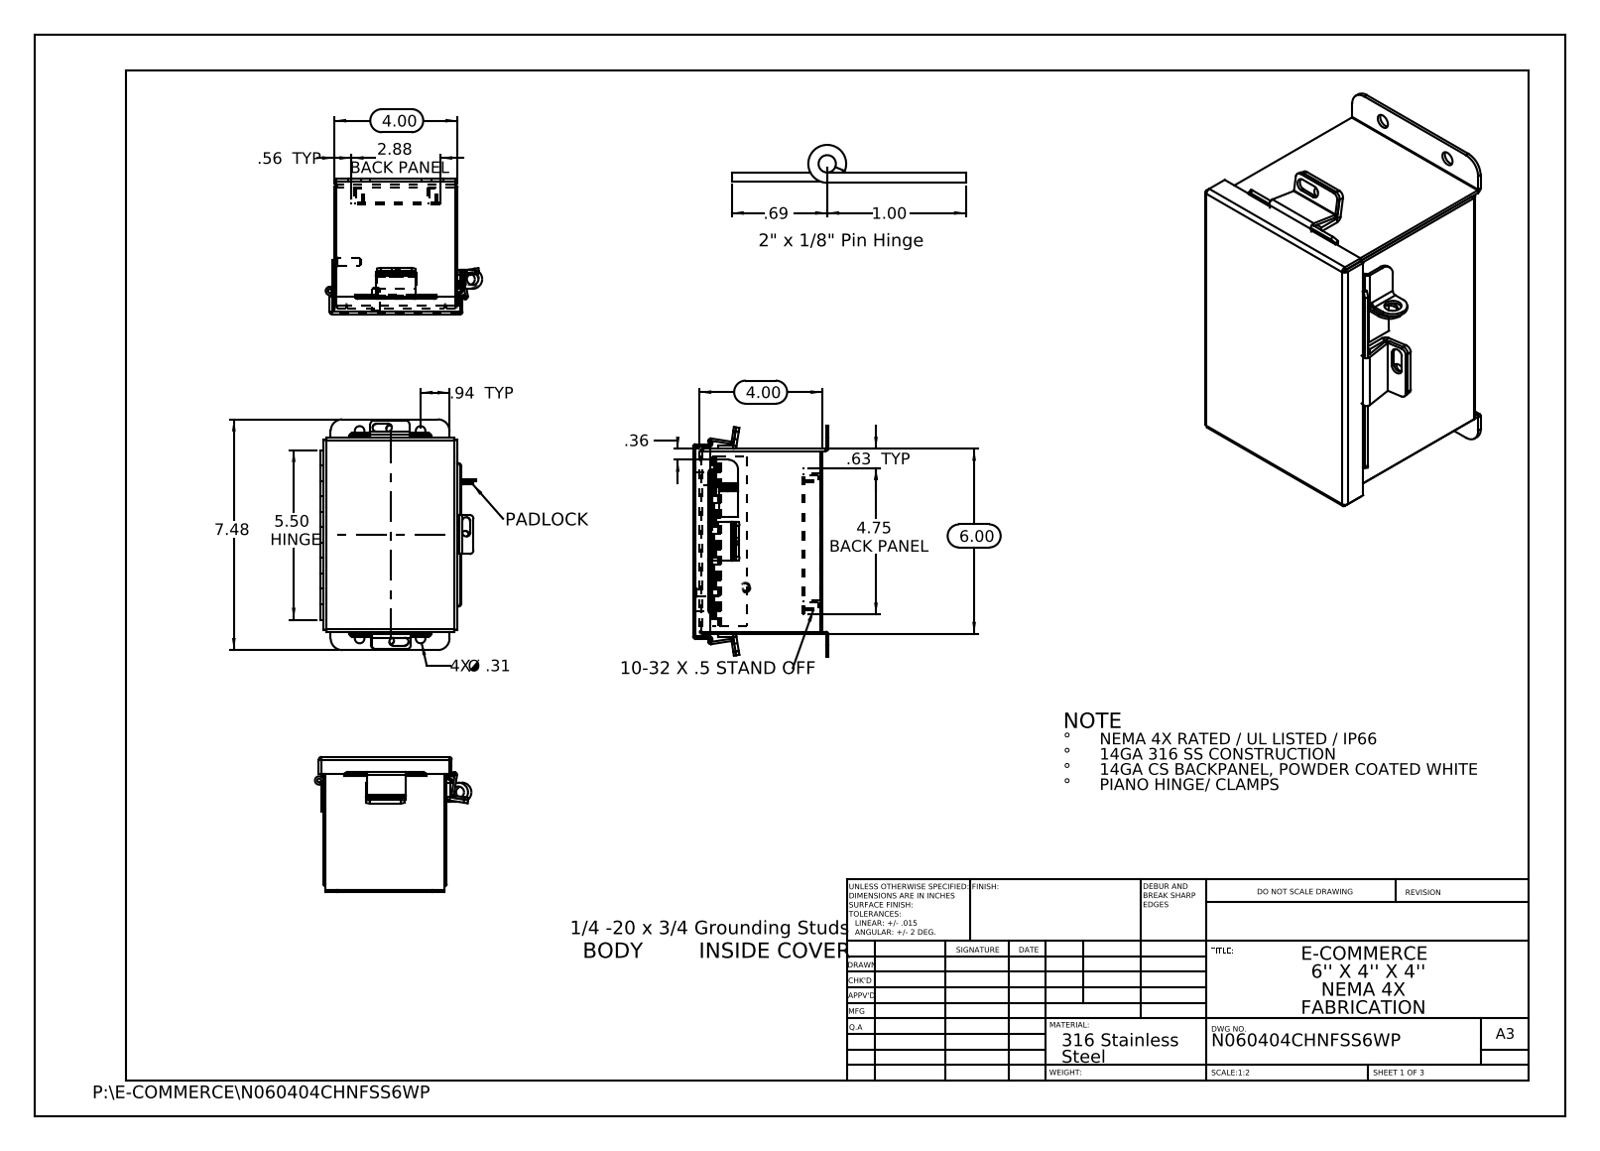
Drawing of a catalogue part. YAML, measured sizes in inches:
part_name: "N060404CHNFSS6WP JIC_Cover_Template; HW-CLH-JH-20154; N060404CHNFSS6WP _JIC Hinge; N060404CHNFSS6WP JIC Enclosure Template (+8 more)"
step_written_by: "SolidWorks 2013 (CONFIG_CONTROL_DESIGN)"
units: inches
bodies: {solids: 21, faces: 540, planar: 343, cylindrical: 177, other: 20}
overall_size: [7.476, 5.072, 4.39]
volume: 14.09
surface_area: 392.2
round_holes:
  - {diameter: 0.25, count: 7}
  - {diameter: 0.187, count: 4}
  - {diameter: 0.312, count: 4}
  - {diameter: 0.125, count: 1}
  - {diameter: 0.125, count: 1}
  - {diameter: 0.373, count: 1}
  - {diameter: 0.375, count: 1}
round_bosses_or_shafts:
  - {diameter: 0.313, count: 4}
  - {diameter: 0.315, count: 2}
  - {diameter: 0.236, count: 2}
  - {diameter: 0.273, count: 1}
  - {diameter: 0.25, count: 1}
partial_cylinders:
  - {radius: 0.013, count: 13}
  - {radius: 0.009, count: 12}
  - {radius: 0.088, count: 12}
  - {radius: 0.125, count: 10}
  - {radius: 0.083, count: 6}
  - {radius: 0.1, count: 6}
  - {radius: 0.133, count: 6}
  - {radius: 0.375, count: 4}
face_to_face_distances: [0.075, 3.925, 4.128, 5.925, 4, 3.85, 4.053, 4.203, 5.85, 6]
hole_center_spacings: [1.315, 2.534, 5.43, 5.846, 1.976, 2.375, 4.126, 4.761]
